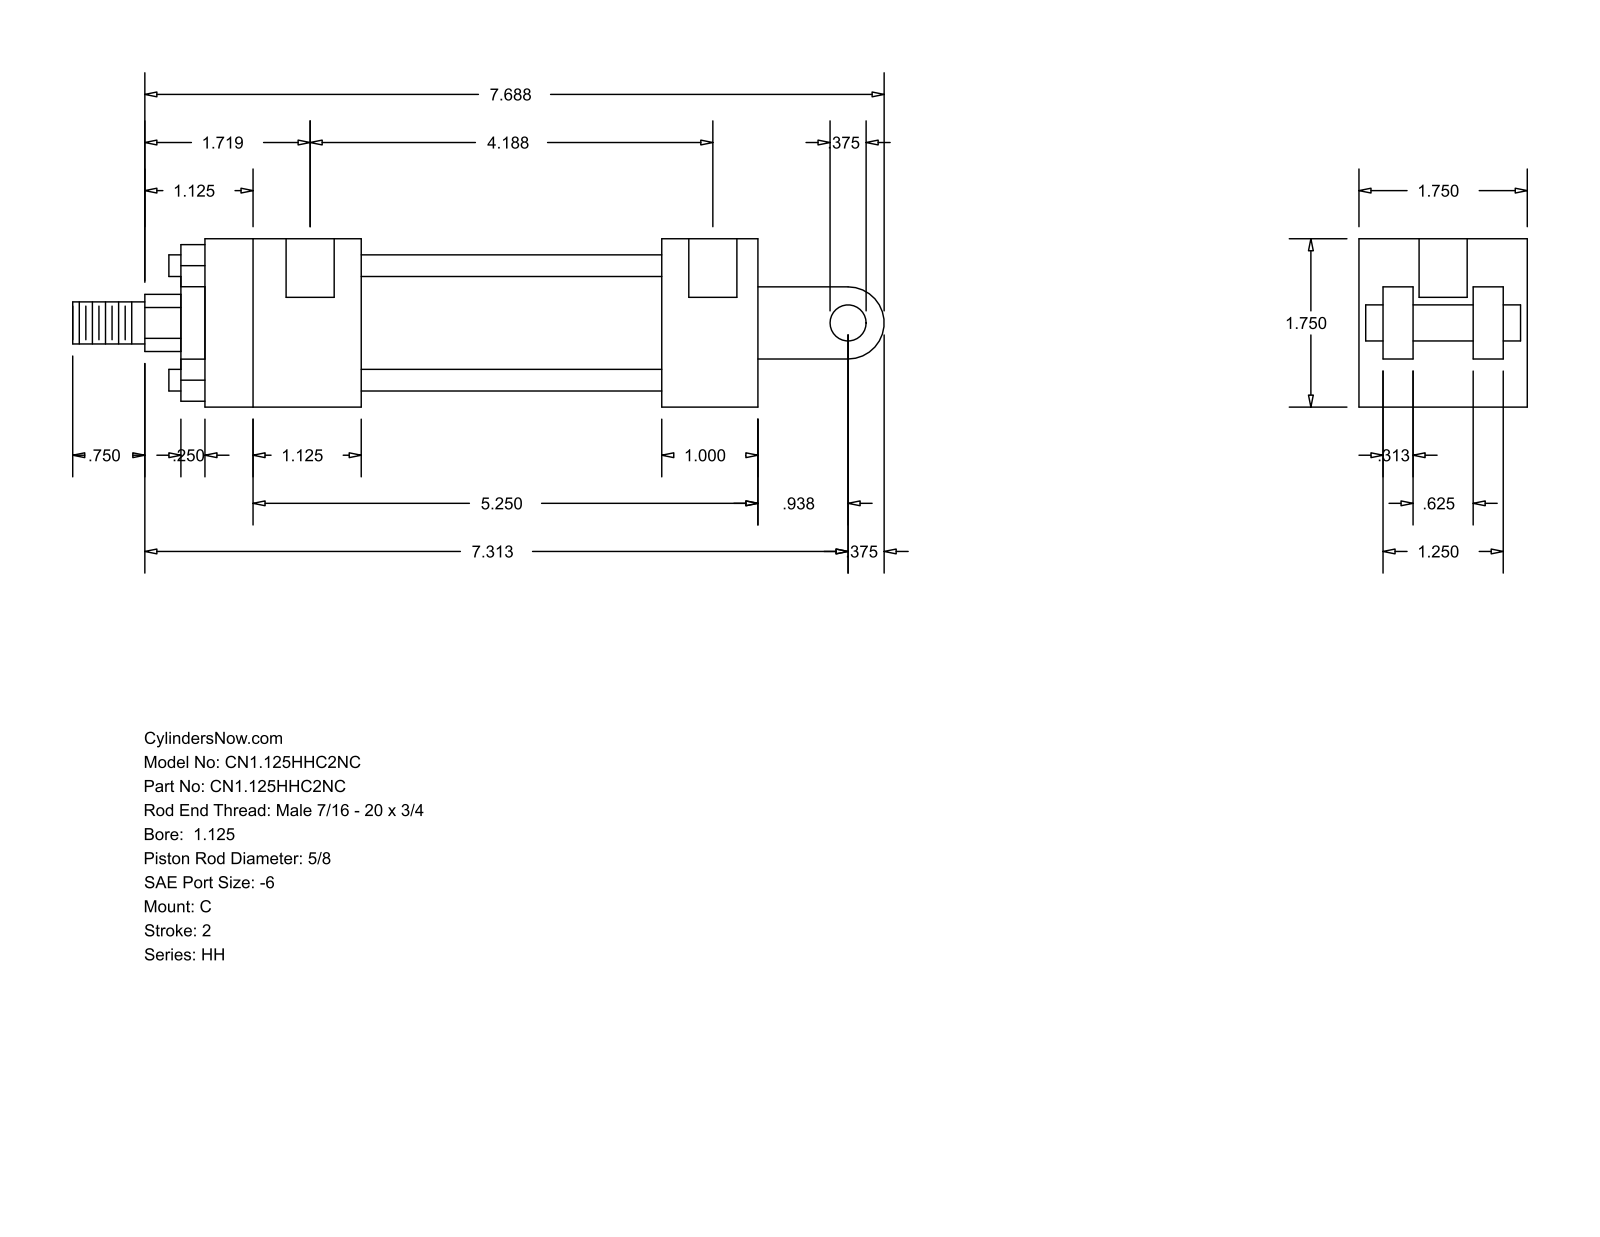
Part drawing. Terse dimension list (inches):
name: HH_C__0112_0.625
written by: GSSL Pune (CONFIG_CONTROL_DESIGN)
unit: in
bodies: 0 solids, 99 faces (70 planar, 29 cylindrical, 0 other)
size: 8.437 × 1.75 × 1.75
holes: 4× ⌀0.219, 2× ⌀0.5
bosses: 4× ⌀0.225, 1× ⌀1.375, 1× ⌀1.125, 1× ⌀0.625, 1× ⌀0.437, 1× ⌀0.375
rounds: 1× R0.297, 1× R0.375
face distances: 1.75, 0.25, 1.25, 0.563, 1, 1.188, 1.5, 0.313, 0.938, 1.625
hole spacings: 4.063, 0.125, 4.187
